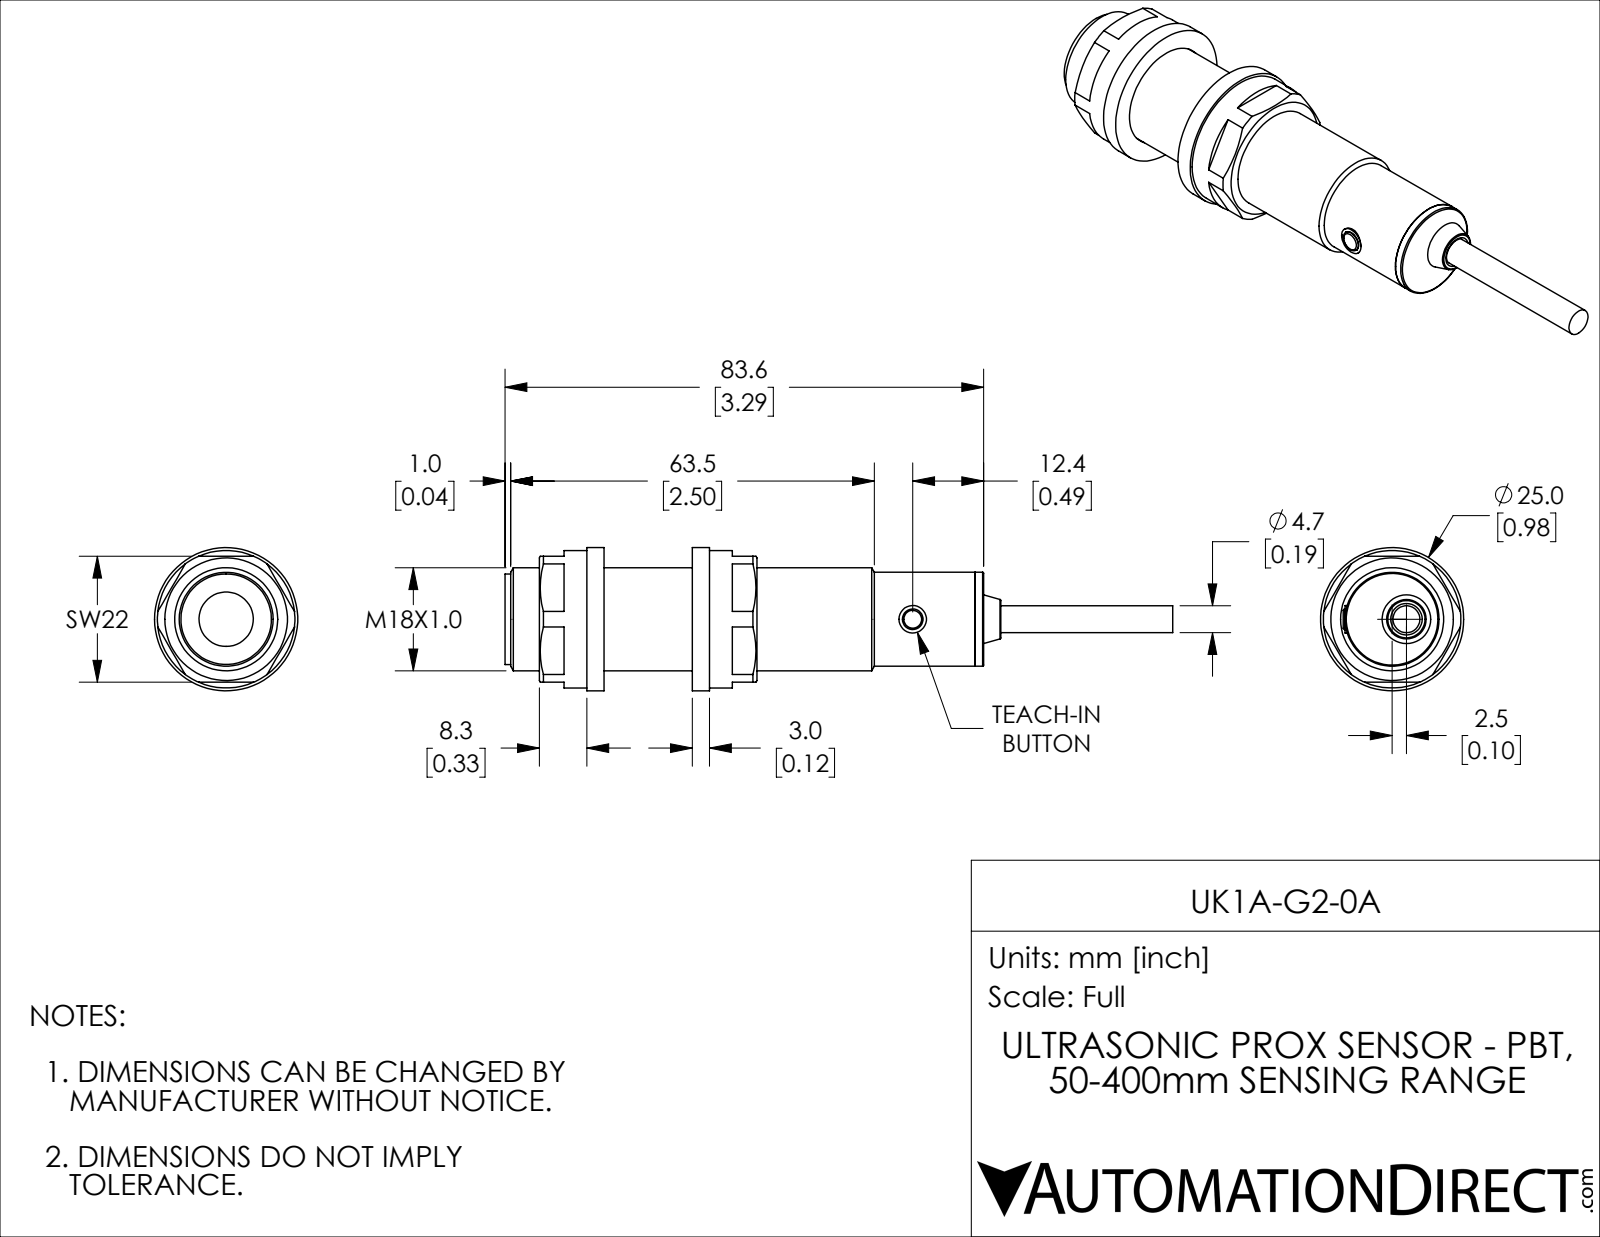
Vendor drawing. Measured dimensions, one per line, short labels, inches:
name: UK1A-G2-0A
written by: SolidWorks 2018 (AUTOMOTIVE_DESIGN)
unit: in
bodies: 10 solids, 107 faces (49 planar, 40 cylindrical, 18 other)
size: 4.591 × 0.984 × 0.984
volume: 1.539 in³; area: 17.7 in²
holes: 2× ⌀0.185, 1× ⌀0.142, 1× ⌀0.374, 1× ⌀0.709, 1× ⌀0.717
bosses: 1× ⌀0.984, 1× ⌀0.945, 1× ⌀0.646, 1× ⌀0.622, 1× ⌀0.213, 1× ⌀0.189
face distances: 0.118, 0.724, 0.843, 2.669, 1.827, 0.524, 1.366, 3.193, 0.642, 2.551
hole spacings: 0.098
